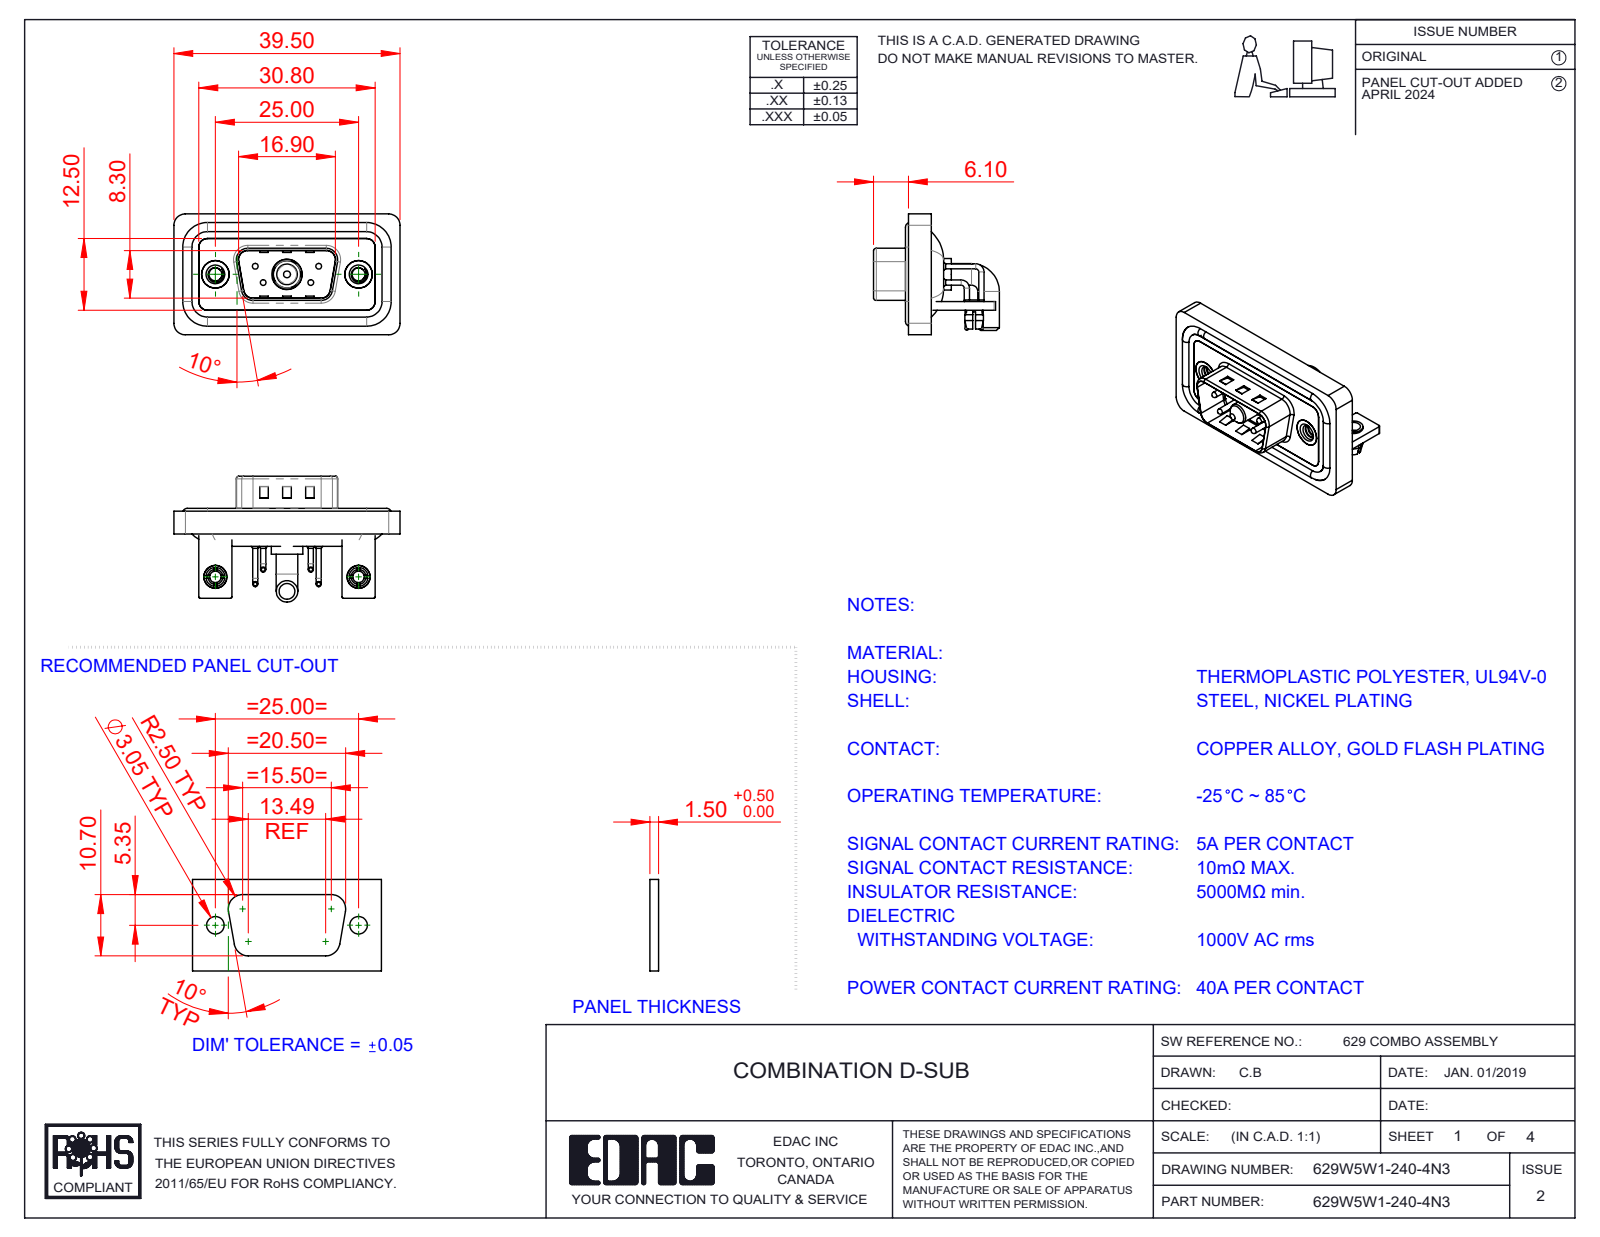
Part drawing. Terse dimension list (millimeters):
name: Power Pin_40A RA; 629Combo Shell Front_09 Contacts; 629Combo Housing_5W1; 629Combo Contact Row 2 (+7 more)
written by: SolidWorks 2023 (CONFIG_CONTROL_DESIGN)
unit: mm
bodies: 17 solids, 1026 faces (479 planar, 395 cylindrical, 152 other)
size: 39.5 × 21.98 × 21.1
volume: 4 863 mm³; area: 8 005 mm²
holes: 6× ⌀2, 4× ⌀0.75, 4× ⌀1.6, 2× ⌀2.26, 2× ⌀2.5, 2× ⌀3.2, 2× ⌀4, 2× ⌀4.8, 2× ⌀5, 1× ⌀4.85, 1× ⌀5.3
bosses: 8× ⌀0.9, 4× ⌀1.6, 4× ⌀1.5, 4× ⌀1, 4× ⌀0.65, 2× ⌀4.9, 2× ⌀4, 2× ⌀3.75
rounds: 19× R2, 18× R1.5, 16× R0.25, 9× R0.5, 8× R1.6, 4× R0.6, 4× R0.65, 4× R0.9
face distances: 0.4, 1.5, 0.8, 2.9, 1.1, 2.1, 1.2, 1.6, 2.5, 3.7
hole spacings: 3.16, 5.72, 7.1, 12.5, 18.1, 25, 4.39, 4.4
